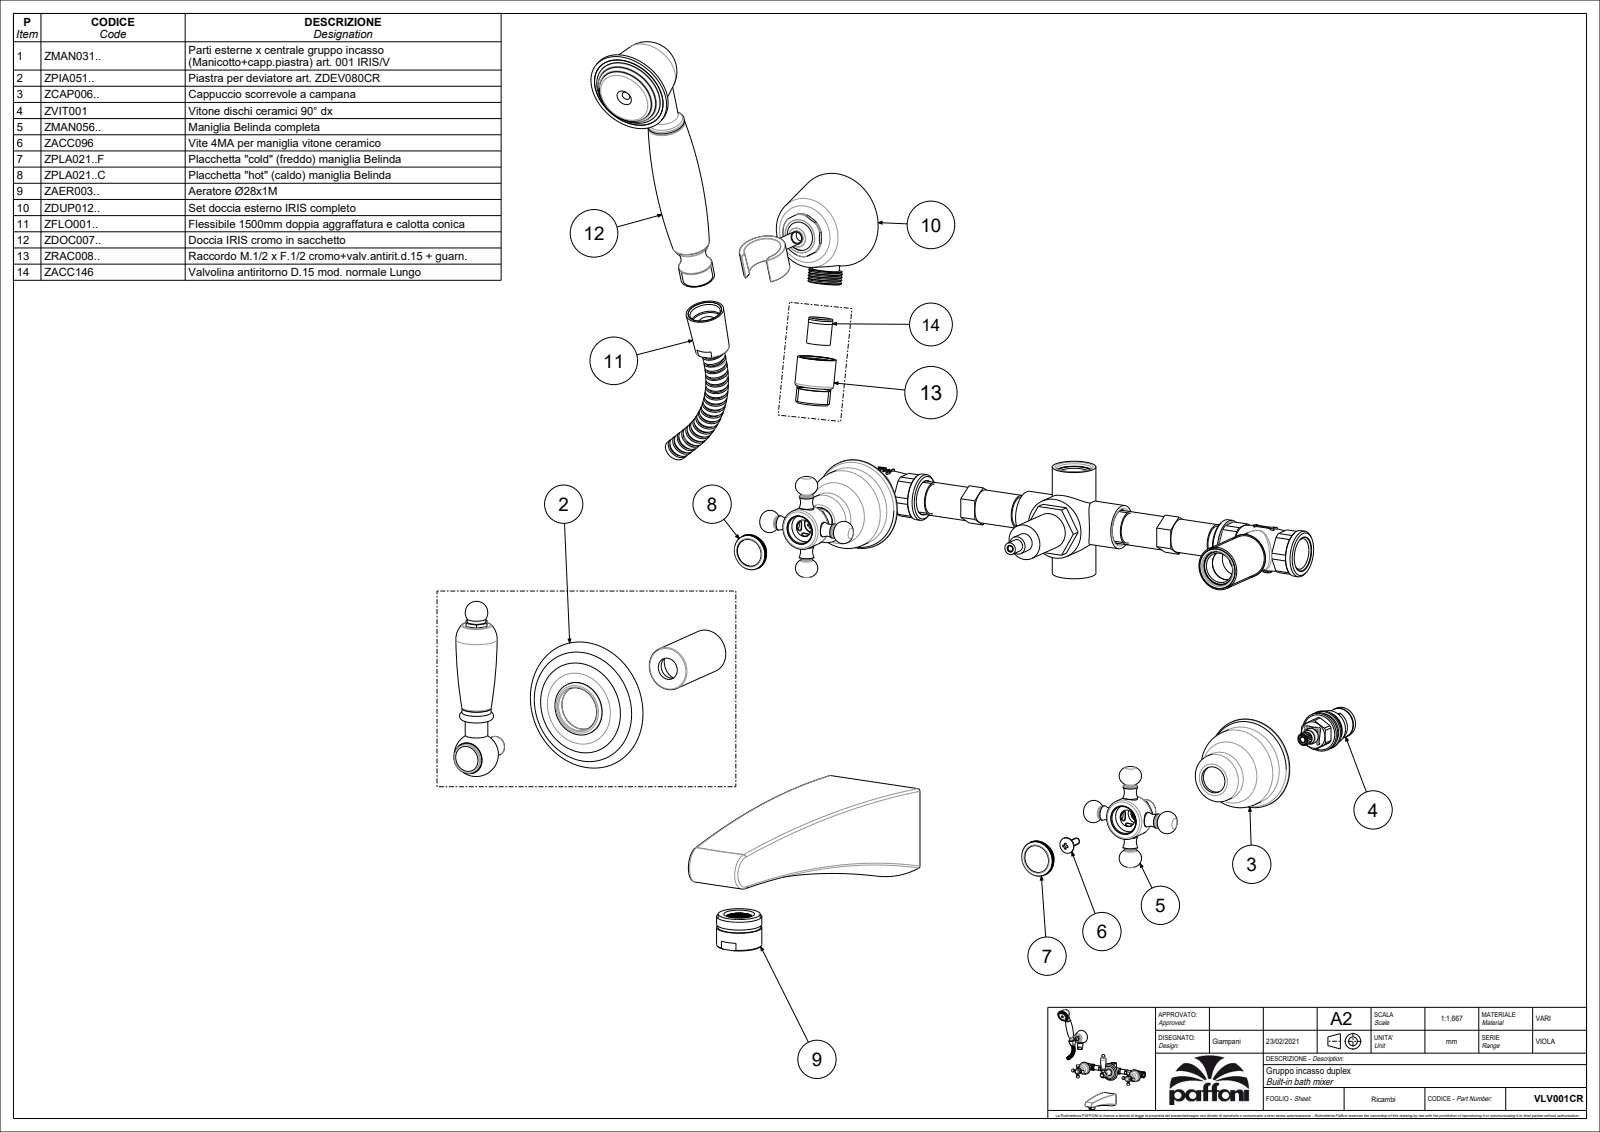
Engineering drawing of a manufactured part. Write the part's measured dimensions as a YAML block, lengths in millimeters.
part_name: "VLV001CR"
step_written_by: "CREO PARAMETRIC BY PTC INC, 2020044 (CONFIG_CONTROL_DESIGN)"
units: millimeters
bodies: {solids: 5, faces: 1179, planar: 498, cylindrical: 342, other: 339}
overall_size: [477.78, 365.12, 200.5]
volume: 883644
surface_area: 144146
round_holes:
  - {diameter: 14.5, count: 1}
  - {diameter: 17, count: 1}
round_bosses_or_shafts:
  - {diameter: 14, count: 4}
  - {diameter: 28, count: 3}
  - {diameter: 9, count: 3}
  - {diameter: 7, count: 3}
  - {diameter: 55, count: 2}
  - {diameter: 49, count: 2}
  - {diameter: 25, count: 2}
  - {diameter: 21, count: 2}
partial_cylinders:
  - {radius: 0.3, count: 6}
  - {radius: 11, count: 2}
  - {radius: 13.25, count: 1}
  - {radius: 13.5, count: 1}
  - {radius: 14.5, count: 1}
face_to_face_distances: [10, 30, 6.01, 40, 58.2, 48.2, 18.2, 5, 13.2, 45]
